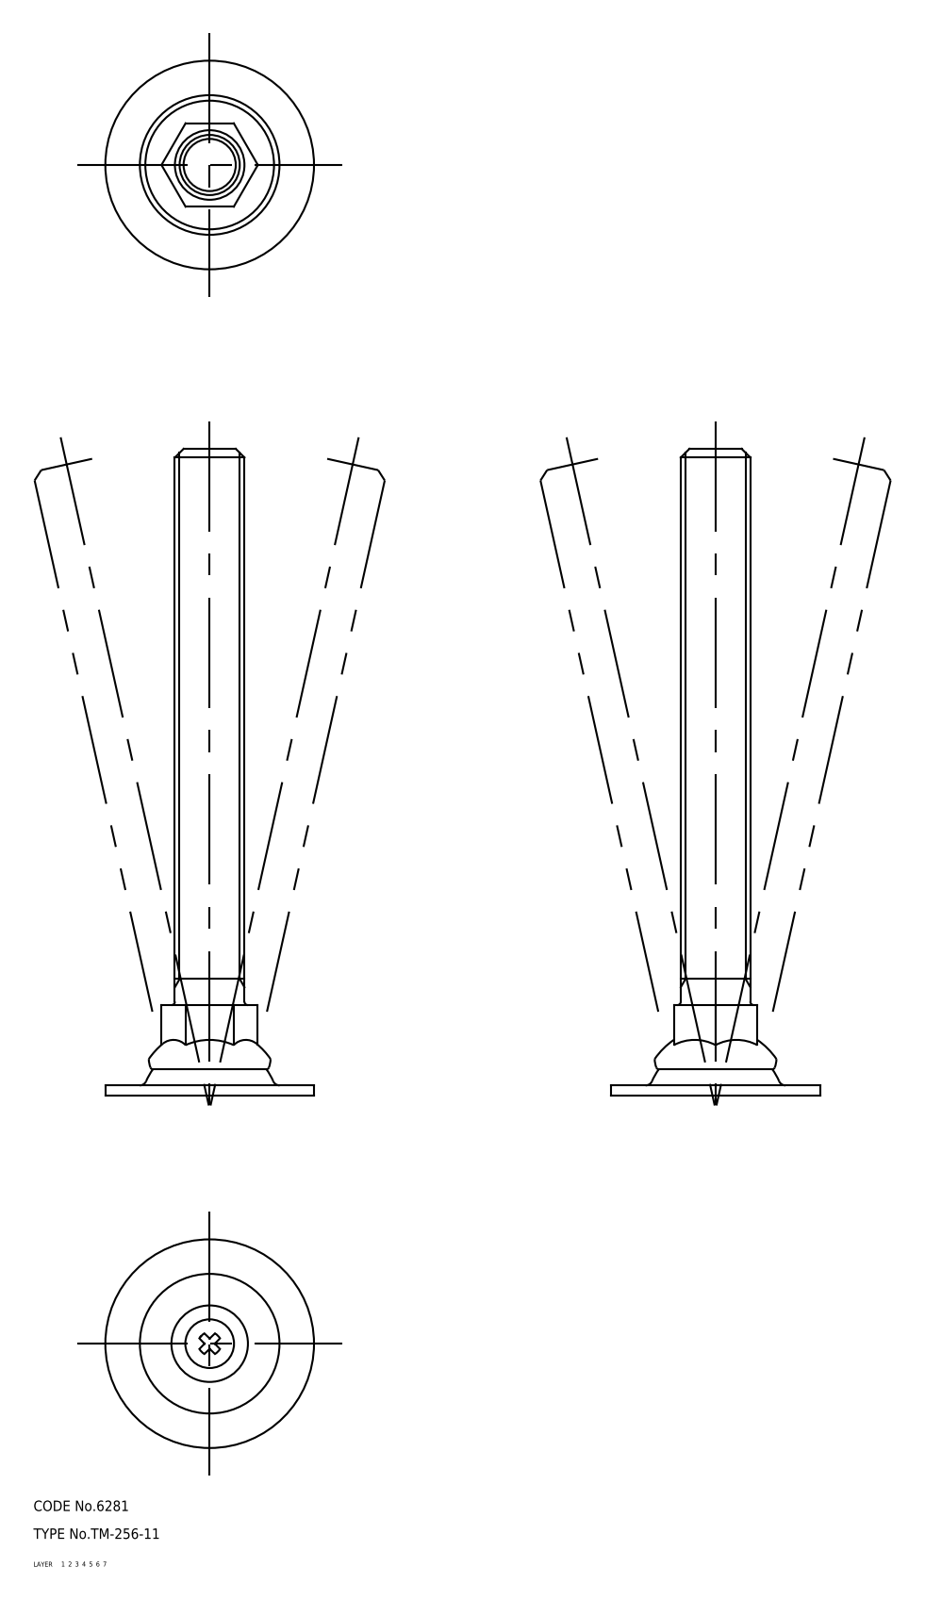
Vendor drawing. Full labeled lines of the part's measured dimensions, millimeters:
Part name (STEP PRODUCT): 67113090; 67113103; 67113116; 67113129
STEP written by: CADfix (AUTOMOTIVE_DESIGN)
Units: millimetres
Bodies: 4 solids, 72 faces (0 planar, 0 cylindrical, 72 other)
Overall size (bounding box): 186 × 60 × 60
Volume: 67 667 mm³ · Surface area: 22 039 mm²
